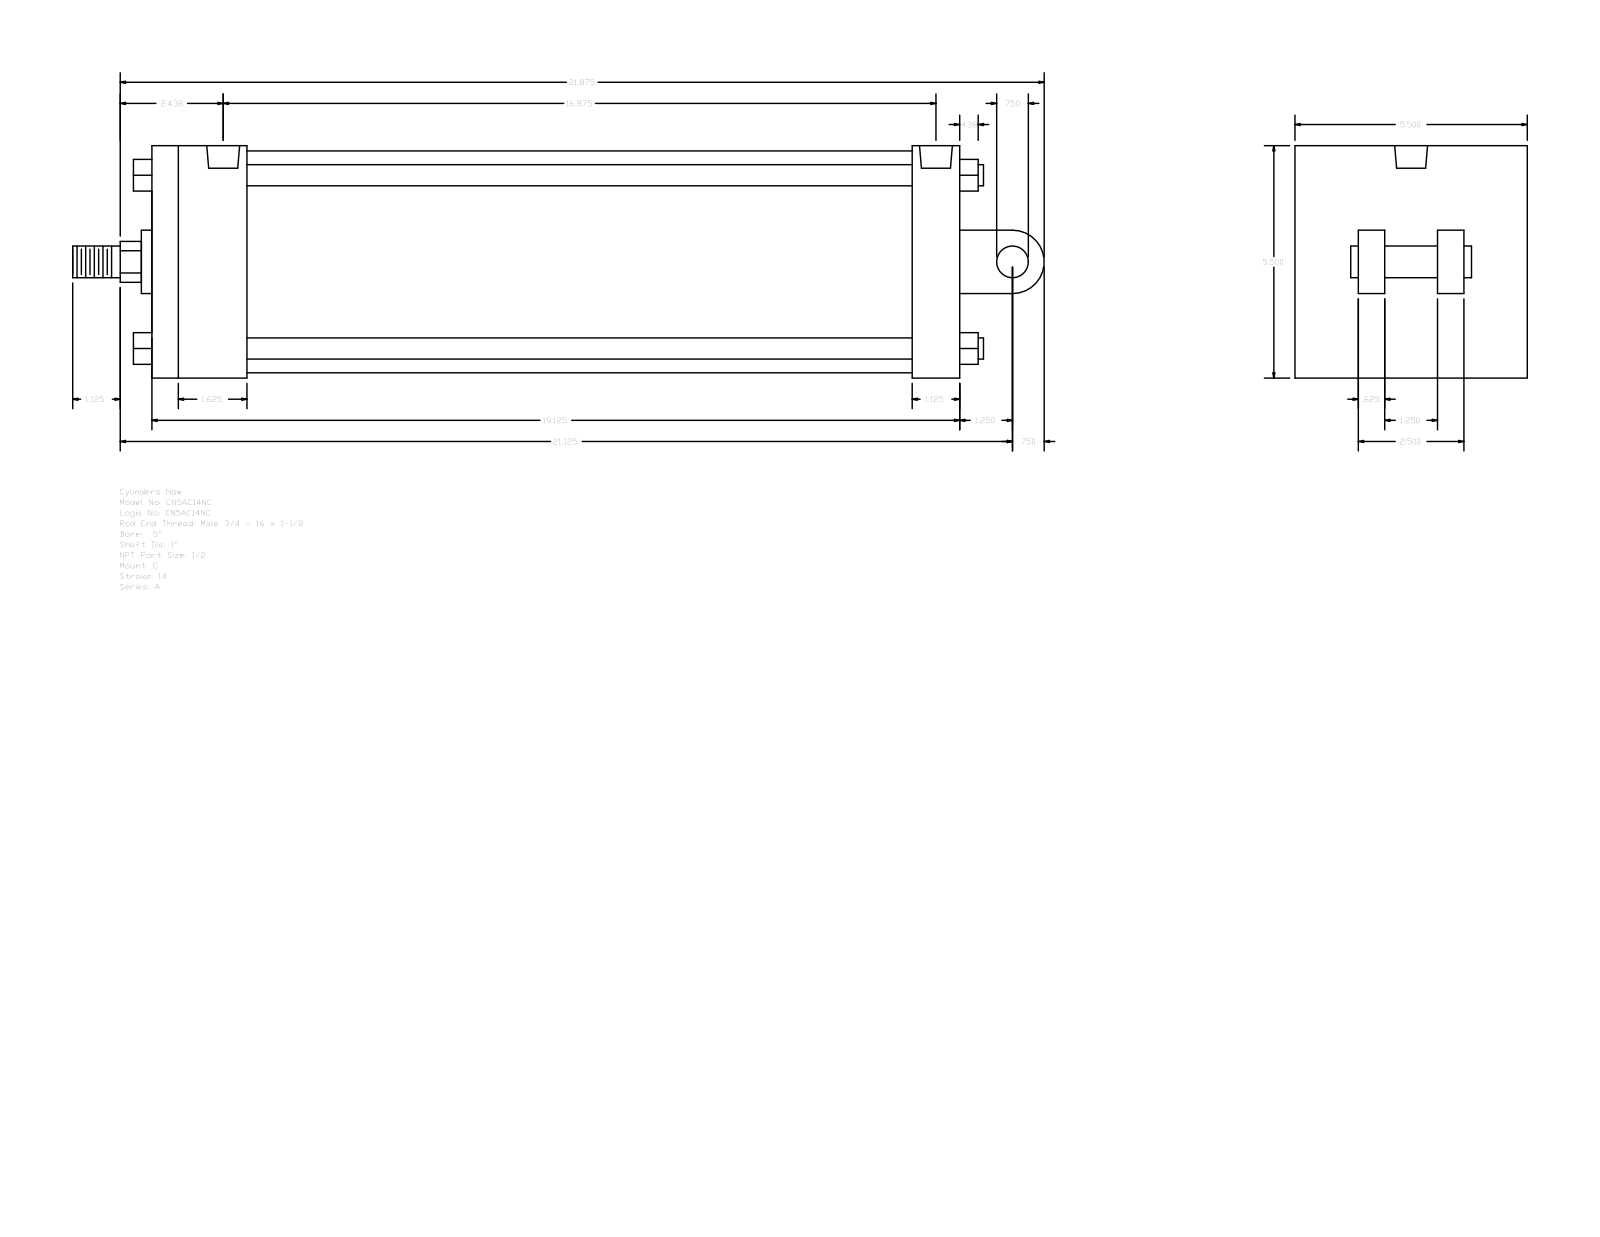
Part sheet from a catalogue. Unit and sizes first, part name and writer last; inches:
Units: inches
Overall size (bounding box): 23 × 5.5 × 5.5
Round holes (diameter × count): ⌀0.344 ×4, ⌀0.778 ×2
Round bosses / shafts (diameter × count): ⌀0.5 ×4, ⌀0.75 ×2, ⌀5.25 ×1, ⌀1.5 ×1, ⌀1 ×1
Partial cylindrical surfaces — rounded edges, fillets, slot ends (radius × count): R0.484 ×1, R0.75 ×1
Main face-to-face distances: 5.5, 19.125, 1.125, 2.25, 18, 15.75, 16.875, 1.5, 2.125, 3.375
Hole centre spacings: 0.094, 16.687, 16.781, 16.875
Bodies: 0 solids, 135 faces (102 planar, 33 cylindrical, 0 other)
Part name (STEP PRODUCT): A_C__0500_1
STEP written by: GSSL Pune (CONFIG_CONTROL_DESIGN)
